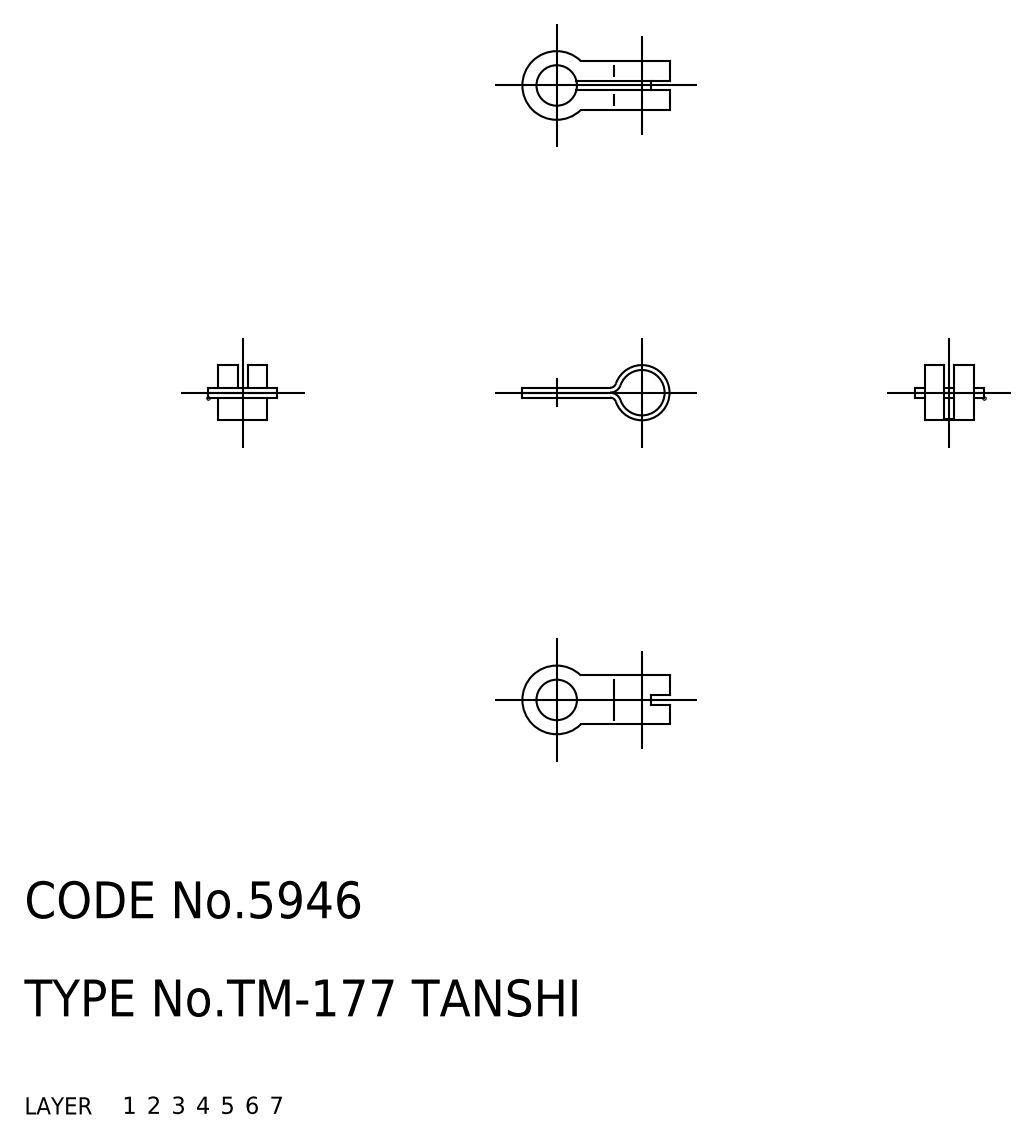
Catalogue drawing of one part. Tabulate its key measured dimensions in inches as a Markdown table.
| quantity | value |
| --- | --- |
| part name | terminal |
| STEP written by | CADfix (AUTOMOTIVE_DESIGN) |
| units | inches |
| bodies | 1 solid, 22 faces (0 planar, 0 cylindrical, 22 other) |
| overall size | 0.472 × 0.22 × 0.177 |
| volume | 0.002 in³ |
| surface area | 0.346 in² |
